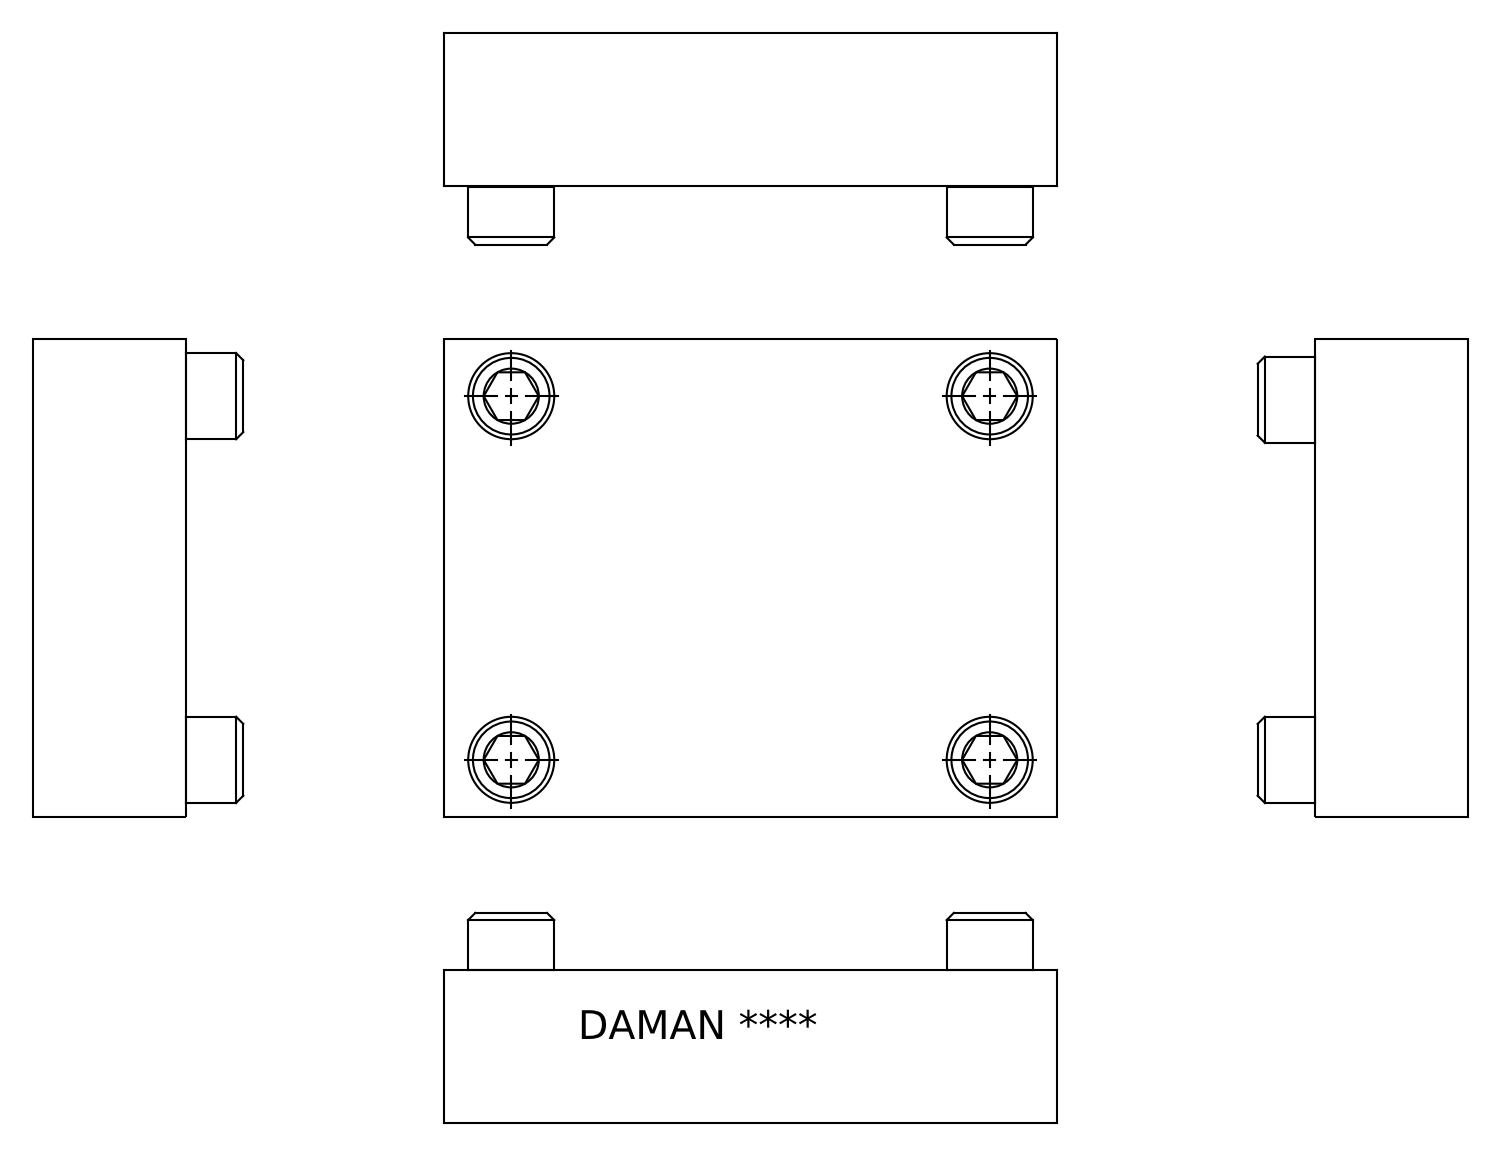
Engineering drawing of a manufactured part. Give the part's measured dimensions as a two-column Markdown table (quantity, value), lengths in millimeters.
| quantity | value |
| --- | --- |
| part name | Part_DP08CPP_3D |
| STEP written by | Autodesk Inventor 2019 (AUTOMOTIVE_DESIGN) |
| units | millimeters |
| bodies | 1 solid, 297 faces (206 planar, 10 cylindrical, 81 other) |
| overall size | 101.6 × 79.38 × 25.4 |
| volume | 193 744 mm³ |
| surface area | 28 913 mm² |
| round holes (diameter × count) | 10.31 × 4, 6.35 × 2, 11.13 × 2, 33.35 × 2 |
| main face-to-face distances | 25.4, 79.38, 1.02, 24.38, 101.6, 100.6, 1, 3.62, 0.64, 0.6 |
| hole center spacings | 43.91, 60.32, 79.37, 99.69, 15.87, 15.9, 21.57, 21.61 |
